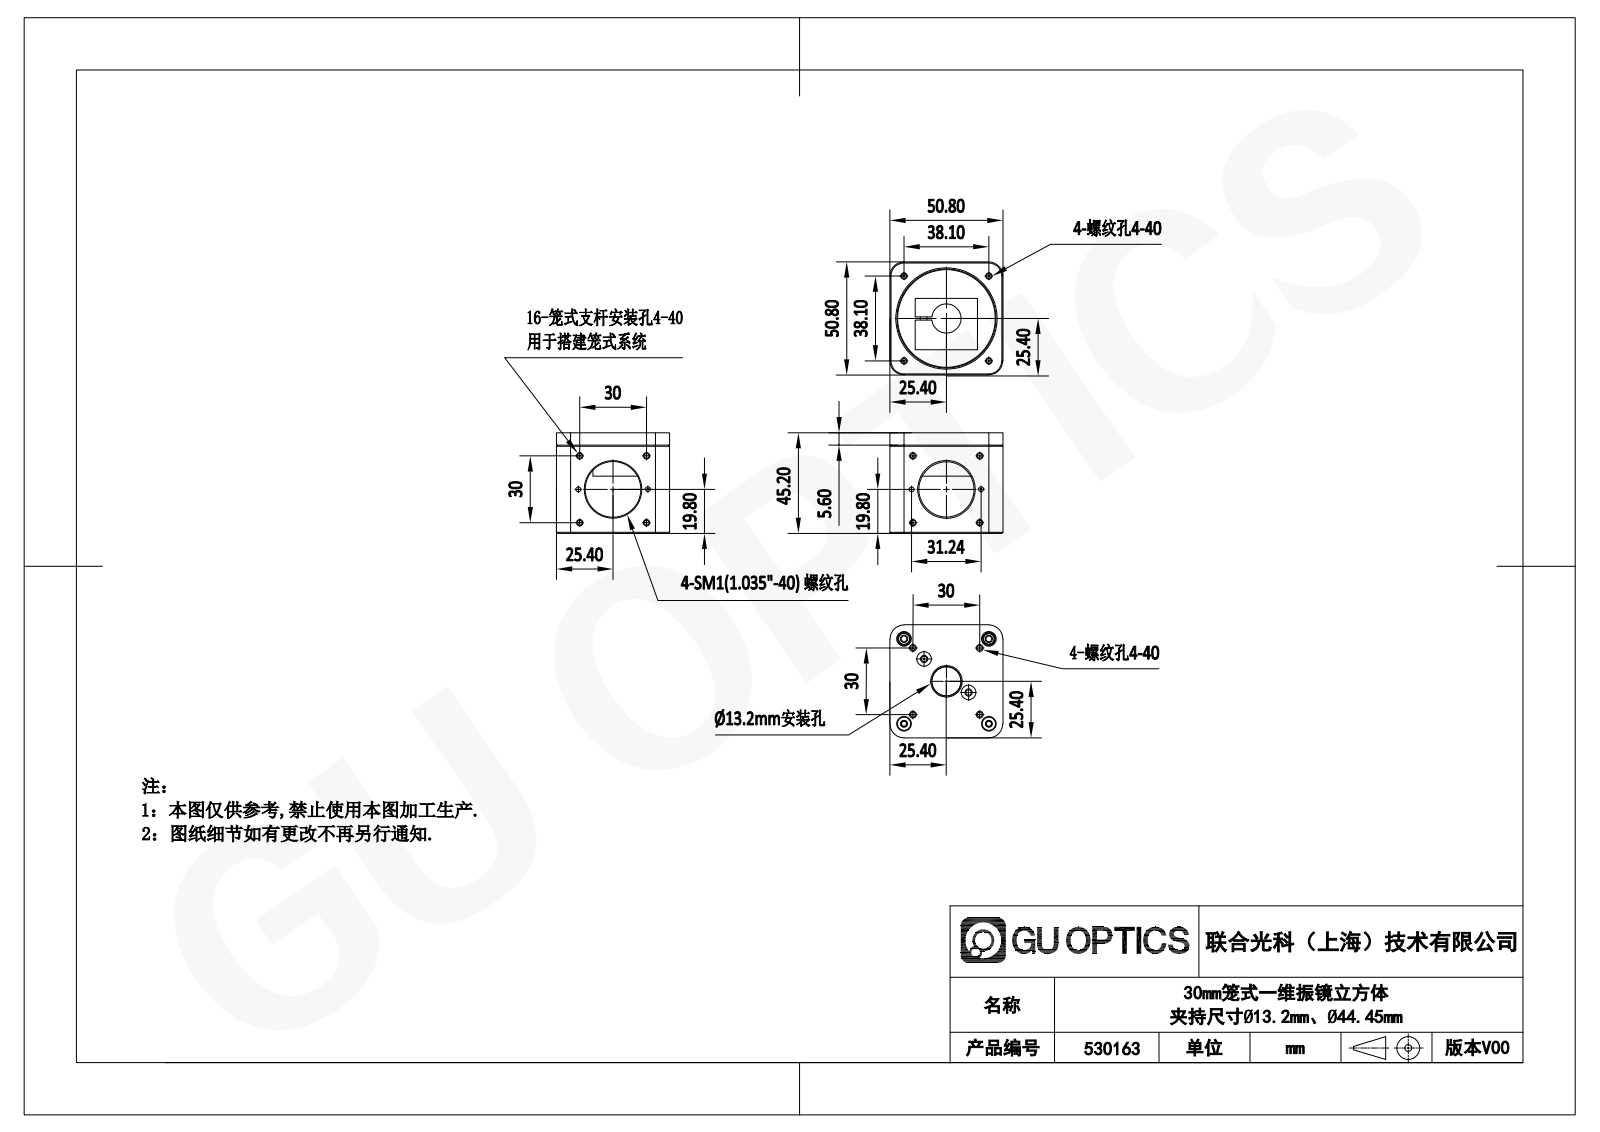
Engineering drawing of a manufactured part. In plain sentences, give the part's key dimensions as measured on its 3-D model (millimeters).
The part is named "530163". Its 3-D file was written by "SolidWorks 2020 (CONFIG_CONTROL_DESIGN)". It is 7 solids with 246 faces: 77 planar, 75 cylindrical and 94 other. Overall it measures 50.8 by 50.8 by 45.2 millimeters. Its volume is 51 157 cubic millimeters and its surface area 25 466 square millimeters. Round holes: 16 of diameter 2.26, 5 of diameter 6, 4 of diameter 2.44, 4 of diameter 3.15, 3 of diameter 2.5, 3 of diameter 3.4, 2 of diameter 25, 1 of diameter 13.16, 1 of diameter 13.2, 1 of diameter 44.5, 1 of diameter 49.53. Round bosses or shafts: 3 of diameter 5.5, 3 of diameter 3, 1 of diameter 45.72. Partial cylindrical surfaces (rounded edges, fillets, slot ends): 4 of radius 6.35. The main face-to-face distances are 50.8, 6.6, 5.6, 1, 39.4, 11.4, 45.2, 39.6, 38.6, 19.5. The hole center spacings are 21.21, 30, 15.01, 34.1, 34.29, 42.43, 5.73, 15.62.
